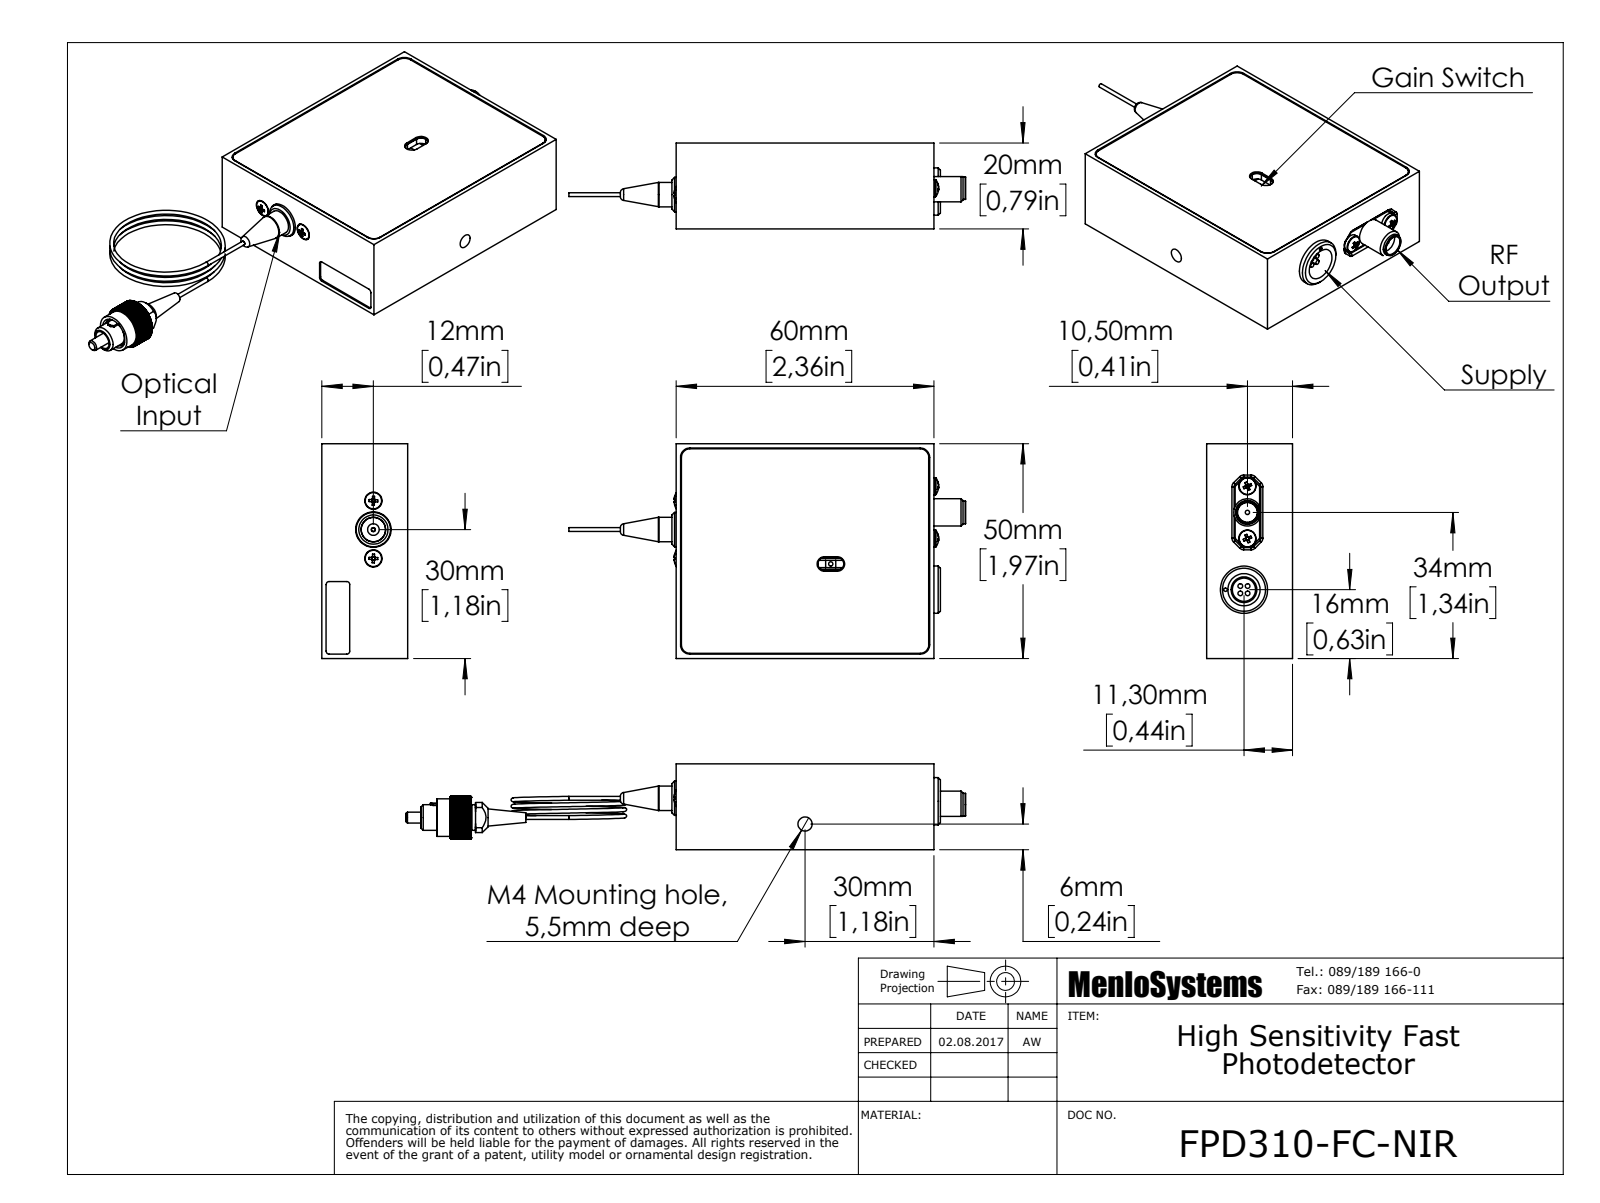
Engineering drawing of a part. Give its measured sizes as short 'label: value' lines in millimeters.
name: FPD310-FC-NIR_170721
written by: SolidWorks 2016 (AUTOMOTIVE_DESIGN)
unit: mm
bodies: 26 solids, 1534 faces (658 planar, 402 cylindrical, 474 other)
size: 130.3 × 56.45 × 20
volume: 39 686 mm³; area: 30 979 mm²
holes: 23× ⌀1.6, 12× ⌀4, 10× ⌀2.2, 2× ⌀2.6, 1× ⌀0.8, 1× ⌀1, 1× ⌀1.1, 1× ⌀1.27, 1× ⌀2.54, 1× ⌀3, 1× ⌀3.2, 1× ⌀3.3
bosses: 15× ⌀2, 12× ⌀3.8, 4× ⌀1.1, 3× ⌀0.85, 2× ⌀4, 2× ⌀0.9, 1× ⌀11, 1× ⌀9.6
rounds: 26× R2.2, 8× R0.7, 8× R0.8, 8× R2, 4× R1.4, 2× R1.5, 2× R1.7, 1× R2.15
face distances: 1.5, 19.55, 0.35, 18.05, 1.85, 19.9, 6.5, 50, 7, 12.9
hole spacings: 4.21, 9.27, 10.5, 14.96, 16.5, 19.36, 20, 21.82
